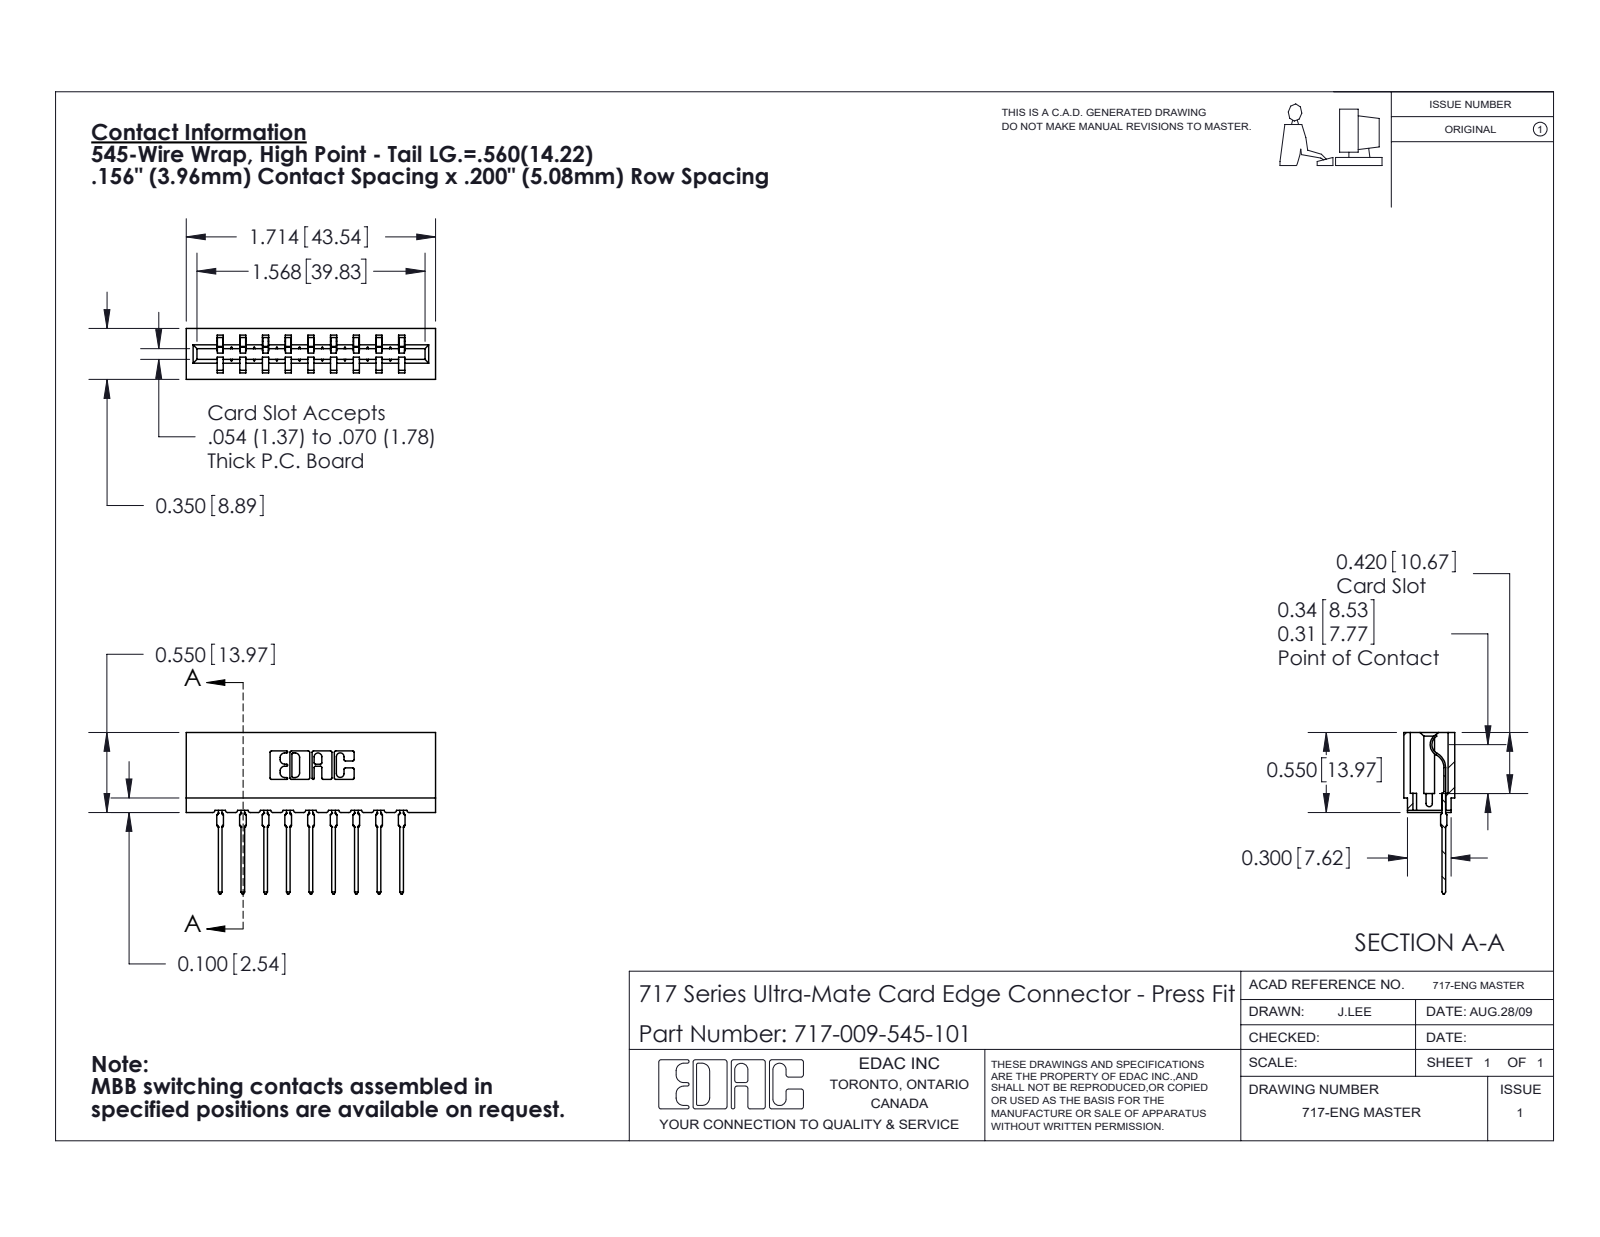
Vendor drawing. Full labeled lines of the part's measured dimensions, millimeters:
Part name (STEP PRODUCT): 717-009-545-101; 717 Part_Insulator Option - 06; 745-292-001_545
STEP written by: SolidWorks 2020 (CONFIG_CONTROL_DESIGN)
Units: millimetres
Bodies: 10 solids, 1111 faces (666 planar, 211 cylindrical, 234 other)
Overall size (bounding box): 43.5 × 28.2 × 8.9
Volume: 3 850 mm³ · Surface area: 5 192 mm²
Partial cylindrical surfaces — rounded edges, fillets, slot ends (radius × count): R0.3 ×22, R0.4 ×18, R0.5 ×18, R0.2 ×6, R0.8 ×6, R0.1 ×4, R0.3 ×4, R0.7 ×3
Main face-to-face distances: 4, 5.4, 15.8, 3.5, 11.9, 5, 8.9, 7.9, 1.1, 7.9
